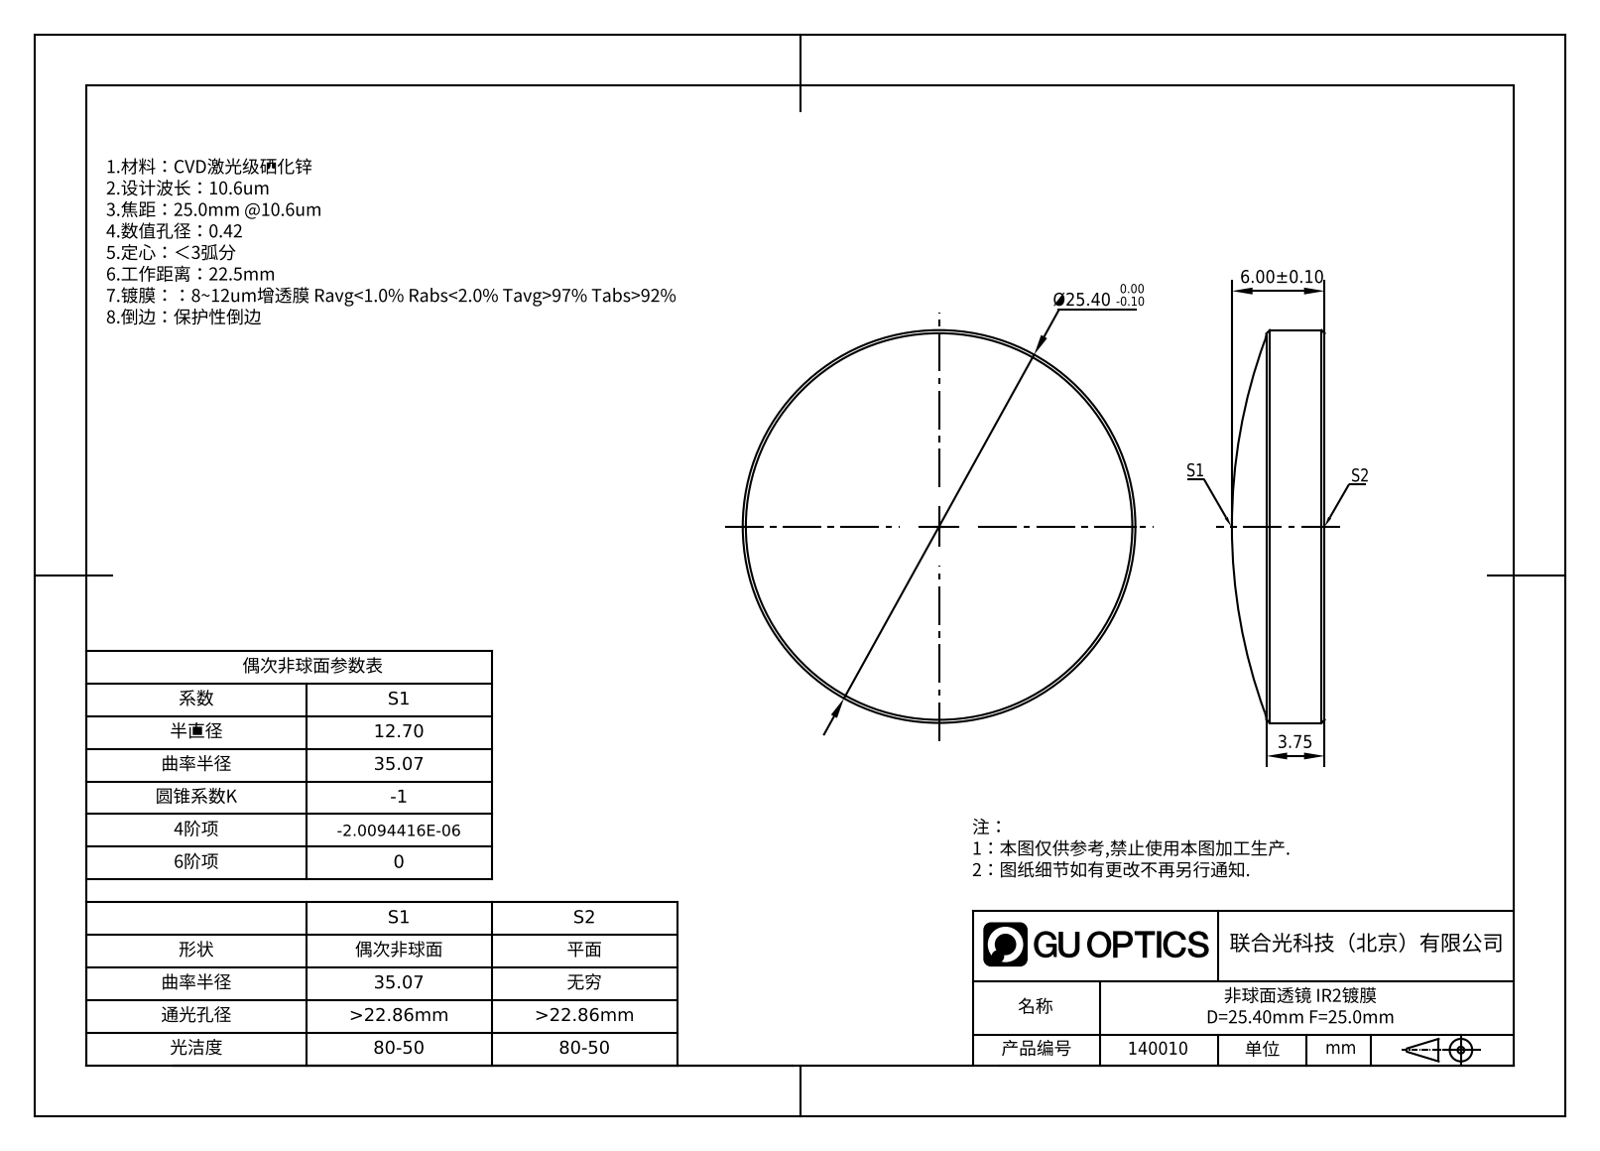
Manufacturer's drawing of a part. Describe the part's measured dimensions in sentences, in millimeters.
The part is named "140010". Its 3-D file was written by "SolidWorks 2020 (CONFIG_CONTROL_DESIGN)". It is 1 solid with 5 faces: 1 planar, 2 cylindrical and 2 other. Overall it measures 25.4 by 25.4 by 6 millimeters. Its volume is 2 467 cubic millimeters and its surface area 1 328 square millimeters. Round bosses or shafts: 1 of diameter 25.4.
